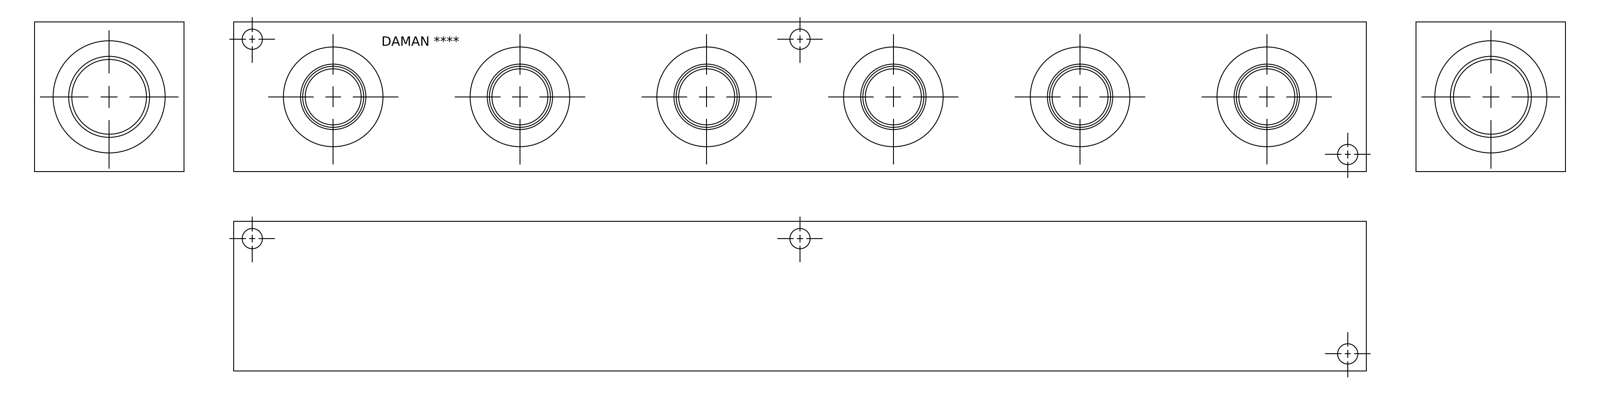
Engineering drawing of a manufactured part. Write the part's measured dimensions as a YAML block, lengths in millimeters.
part_name: "Part_+H0000616S_3D"
step_written_by: "Autodesk Inventor 2020 (AUTOMOTIVE_DESIGN)"
units: millimeters
bodies: {solids: 1, faces: 433, planar: 221, cylindrical: 57, other: 155}
overall_size: [577.85, 76.2, 76.2]
volume: 3036000
surface_area: 230780
round_holes:
  - {diameter: 10.31, count: 6}
  - {diameter: 28.57, count: 6}
  - {diameter: 31.27, count: 6}
  - {diameter: 33.76, count: 6}
  - {diameter: 49.12, count: 6}
  - {diameter: 33.35, count: 5}
  - {diameter: 35.51, count: 5}
  - {diameter: 33.34, count: 1}
  - {diameter: 38.1, count: 1}
  - {diameter: 39.22, count: 1}
  - {diameter: 41.27, count: 1}
  - {diameter: 41.28, count: 1}
face_to_face_distances: [76.2, 0.79, 75.41, 577.85, 577.06, 576.27, 19.84, 19.05, 56.36, 558.01]
hole_center_spacings: [95.25, 190.5, 285.75, 279.4, 285.5, 381, 561.88, 50.65]
